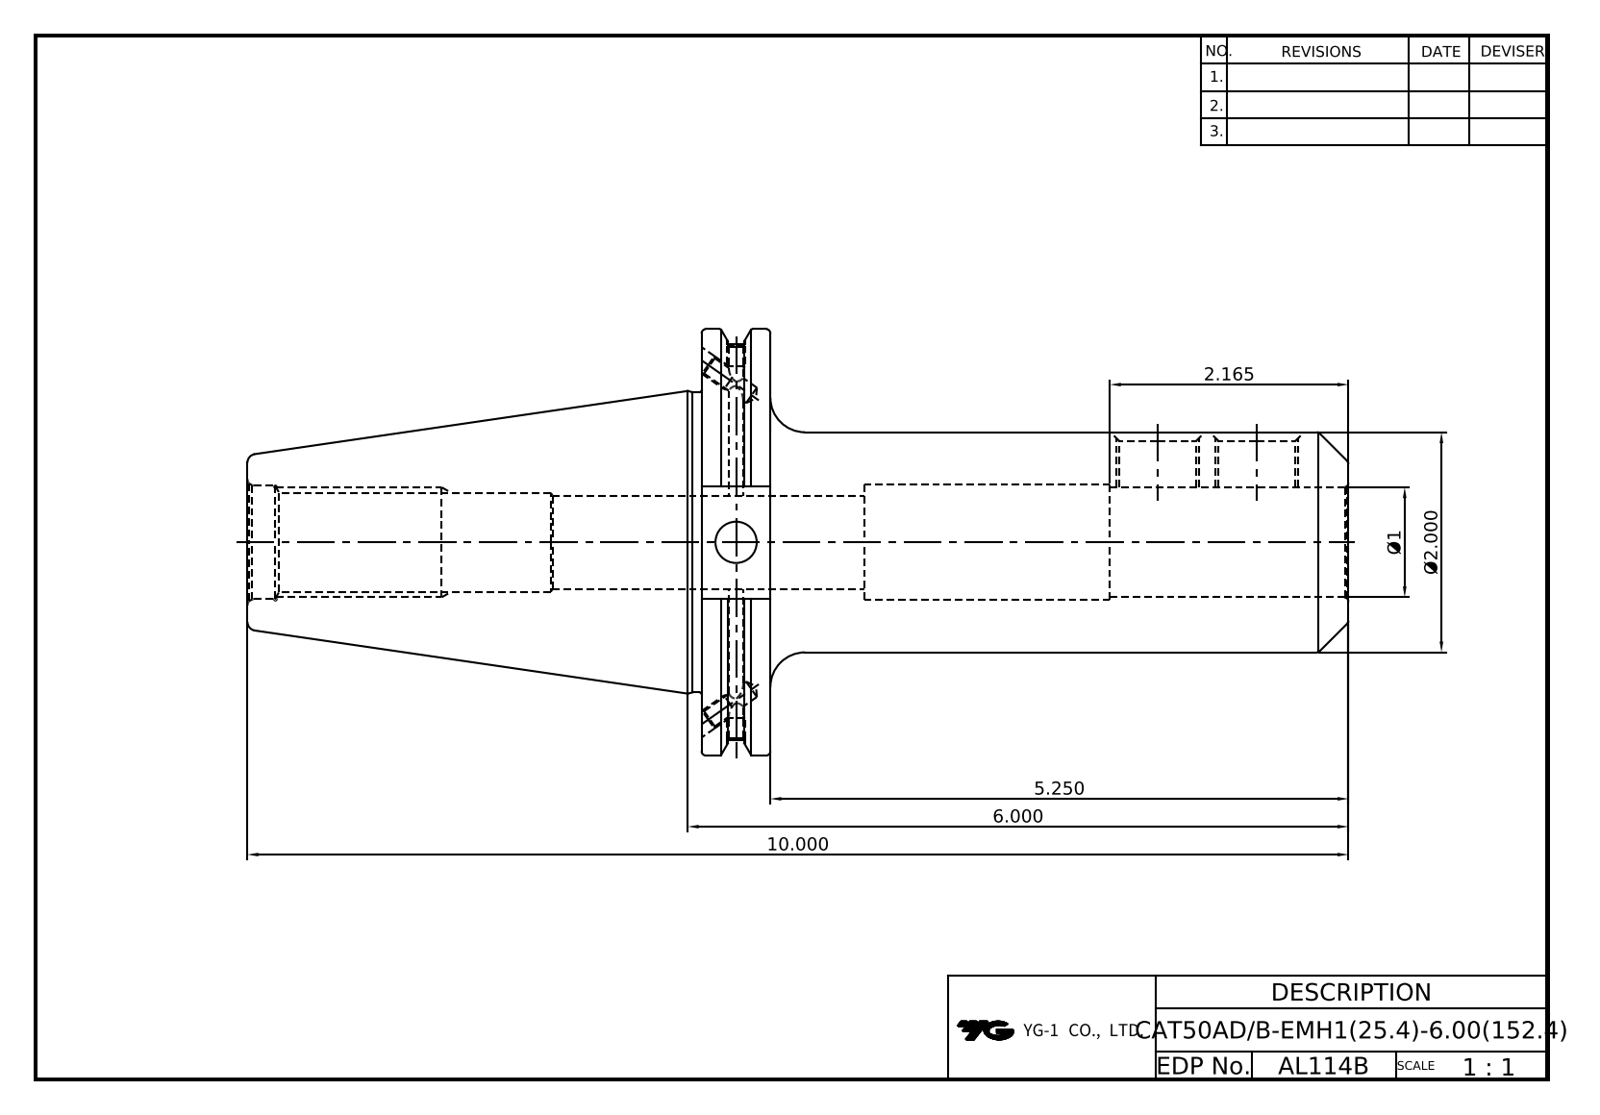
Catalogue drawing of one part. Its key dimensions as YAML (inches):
part_name: "LO-CAT50ADB-EMH25.4-152.4"
step_written_by: "Autodesk Inventor 2025 (AUTOMOTIVE_DESIGN)"
units: inches
bodies: {solids: 1, faces: 89, planar: 39, cylindrical: 27, other: 23}
overall_size: [10, 3.875, 3.728]
volume: 31.31
surface_area: 117.5
round_holes:
  - {diameter: 0.128, count: 2}
  - {diameter: 0.163, count: 2}
  - {diameter: 0.165, count: 2}
  - {diameter: 0.197, count: 2}
  - {diameter: 0.682, count: 2}
  - {diameter: 0.375, count: 1}
  - {diameter: 0.865, count: 1}
  - {diameter: 1, count: 1}
  - {diameter: 1.031, count: 1}
  - {diameter: 1.047, count: 1}
round_bosses_or_shafts:
  - {diameter: 3.875, count: 1}
  - {diameter: 3.594, count: 1}
  - {diameter: 2.726, count: 1}
  - {diameter: 2, count: 1}
face_to_face_distances: [0.625, 4.125, 4.75, 10, 5.875, 5.25, 2.875, 1.02, 4.363, 0.238]
hole_center_spacings: [0.902]
